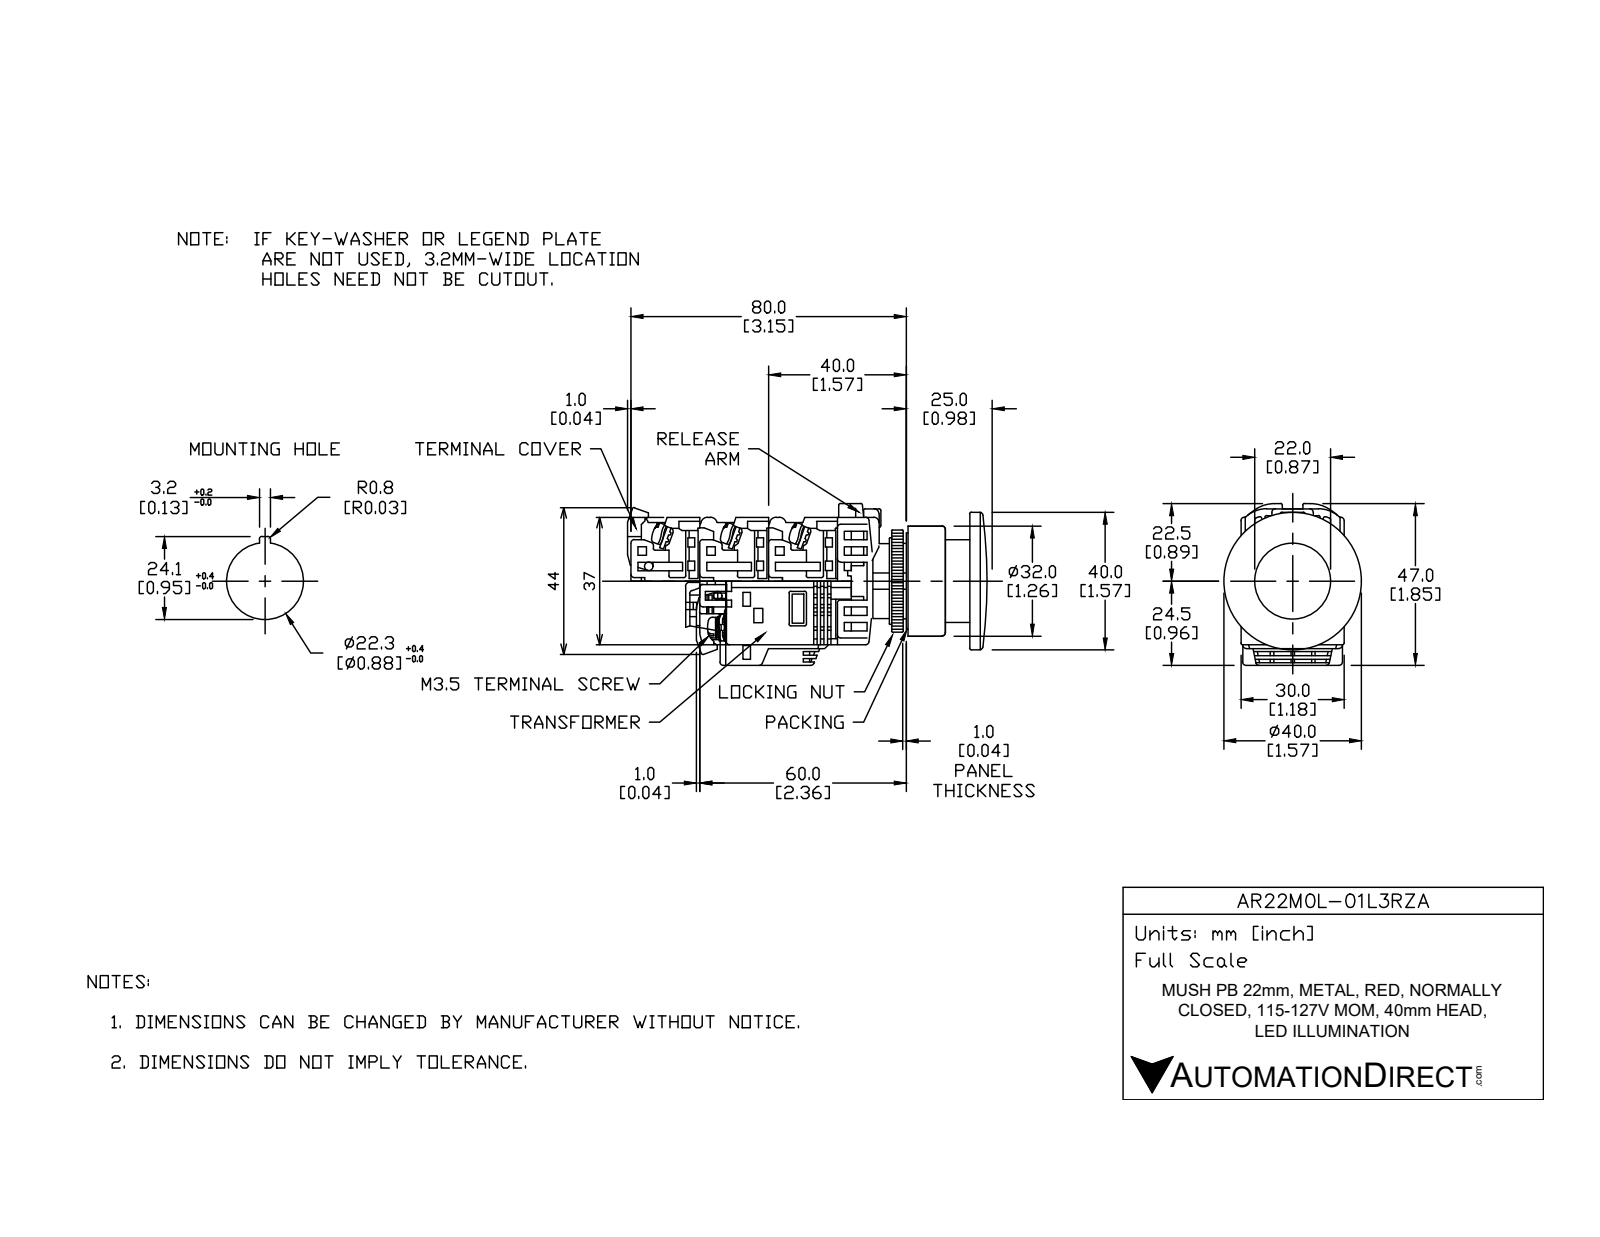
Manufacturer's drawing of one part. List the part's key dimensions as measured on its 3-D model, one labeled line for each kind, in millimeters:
Part name (STEP PRODUCT): AR22M0L-01L3RZA
STEP written by: SolidWorks 2017 (AUTOMOTIVE_DESIGN)
Units: millimetres
Bodies: 18 solids, 444 faces (298 planar, 113 cylindrical, 33 other)
Overall size (bounding box): 86.5 × 43.81 × 40
Volume: 56 810 mm³ · Surface area: 28 630 mm²
Round holes (diameter × count): ⌀21.8 ×1, ⌀22 ×1, ⌀25 ×1, ⌀31 ×1
Round bosses / shafts (diameter × count): ⌀5 ×4, ⌀40 ×1, ⌀32 ×1, ⌀30.5 ×1, ⌀29.8 ×1, ⌀24 ×1, ⌀23.8 ×1, ⌀21.75 ×1
Partial cylindrical surfaces — rounded edges, fillets, slot ends (radius × count): R0.5 ×39, R1.75 ×8, R5 ×4, R4 ×2, R16.59 ×1, R17.59 ×1
Main face-to-face distances: 1, 18, 28.5, 10, 29, 20, 21, 38.5, 3, 2
